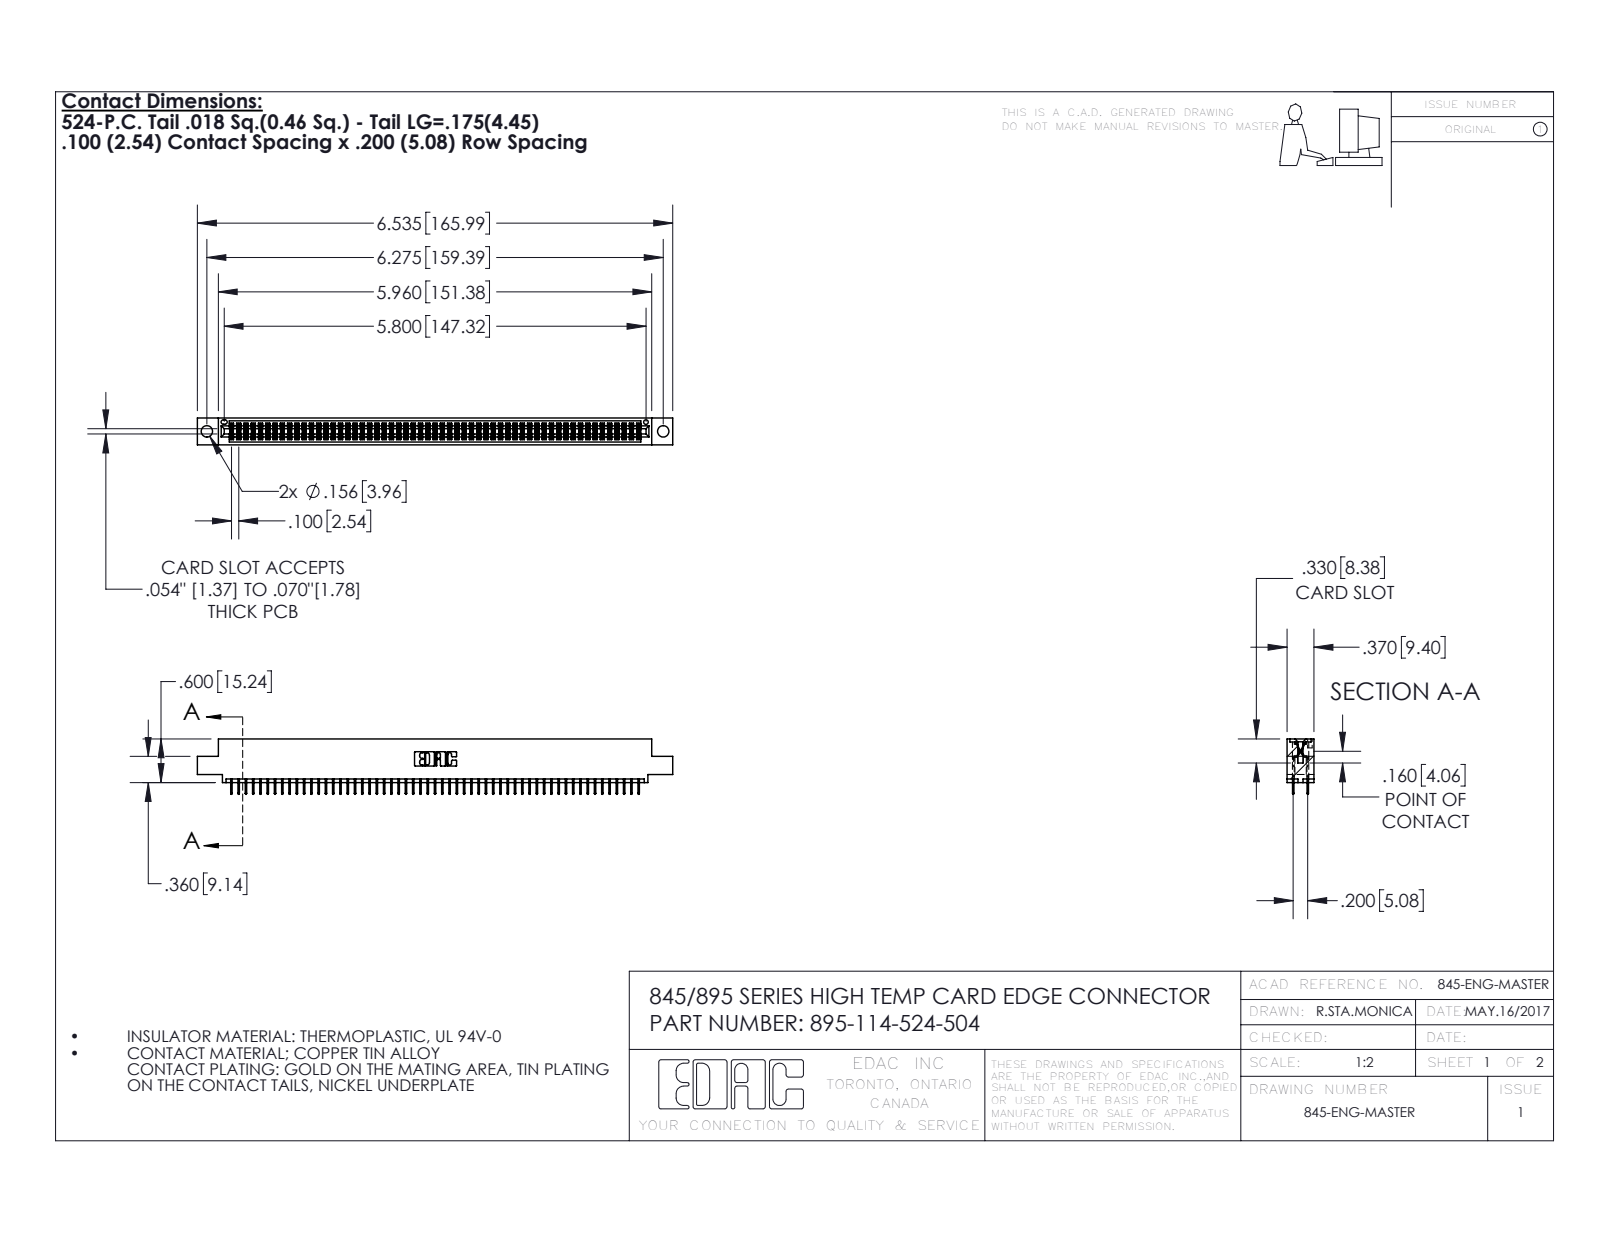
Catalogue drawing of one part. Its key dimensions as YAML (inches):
part_name: "345 Part_0.110 Offset - 0.156 Dia-TH; 395-114-524-504; 345-292-001_345-293-124"
step_written_by: "SolidWorks 2016 (CONFIG_CONTROL_DESIGN)"
units: inches
bodies: {solids: 115, faces: 6286, planar: 4530, cylindrical: 1756, other: 0}
overall_size: [6.535, 0.762, 0.37]
volume: 0.972
surface_area: 36.1
round_holes:
  - {diameter: 0.156, count: 2}
  - {diameter: 0.064, count: 1}
partial_cylinders:
  - {radius: 0.006, count: 171}
  - {radius: 0.01, count: 22}
  - {radius: 0.007, count: 6}
  - {radius: 0.031, count: 6}
  - {radius: 0.026, count: 3}
  - {radius: 0.014, count: 2}
  - {radius: 0.019, count: 2}
  - {radius: 0.022, count: 2}
face_to_face_distances: [0.072, 0.298, 0.2, 0.37, 0.098, 0.272, 0.025, 0.225, 0.072, 0.175]
hole_center_spacings: [0.27, 6.039, 6.275]
